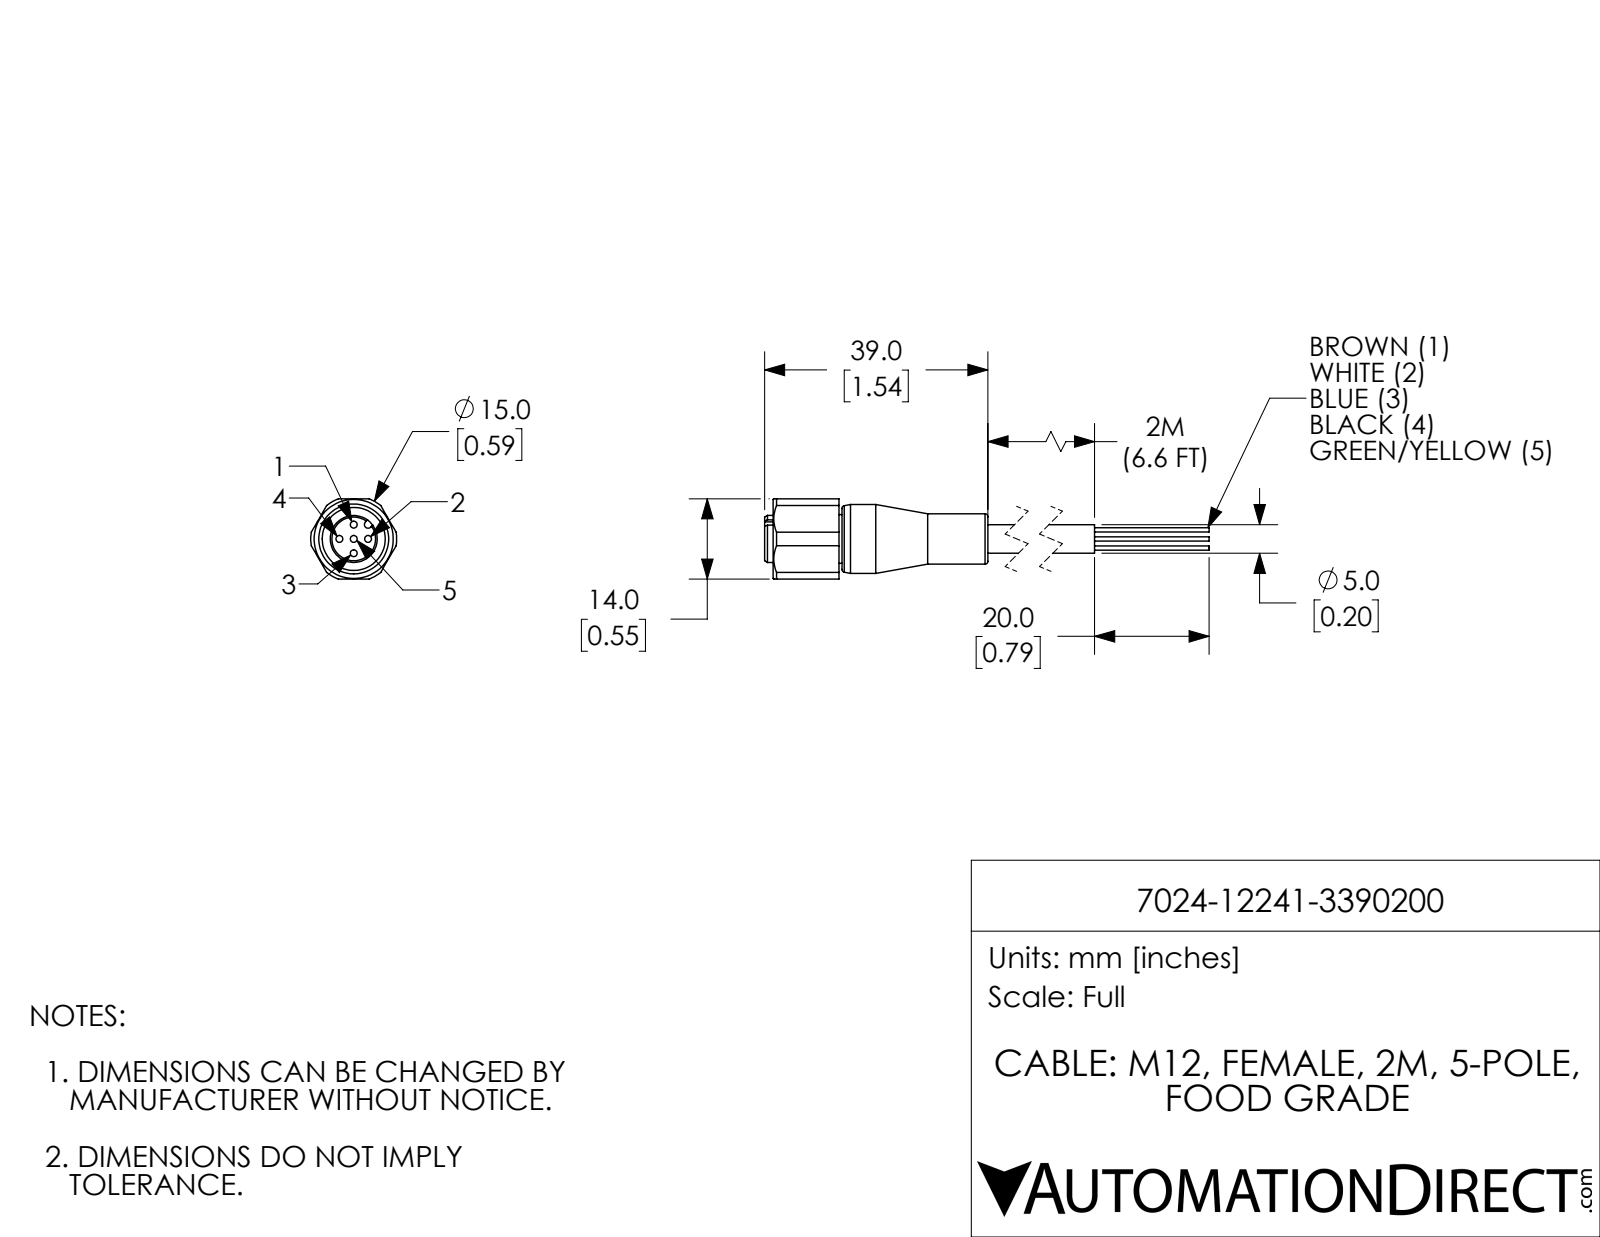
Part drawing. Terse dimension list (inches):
name: 7024-12241-3390200
written by: SolidWorks 2018 (AUTOMOTIVE_DESIGN)
unit: in
bodies: 1 solid, 80 faces (26 planar, 39 cylindrical, 15 other)
size: 3.063 × 0.591 × 0.551
volume: 0.252 in³; area: 4.458 in²
holes: 5× ⌀0.047, 1× ⌀0.433
bosses: 5× ⌀0.03, 1× ⌀0.472, 1× ⌀0.346, 1× ⌀0.335, 1× ⌀0.323, 1× ⌀0.197
rounds: 1× R0.026, 1× R0.295
face distances: 0.551, 0.157, 0.354, 0.512, 0.059, 0.295, 0.453, 0.531, 0.472, 0.177
hole spacings: 0.098, 0.139, 0.197
